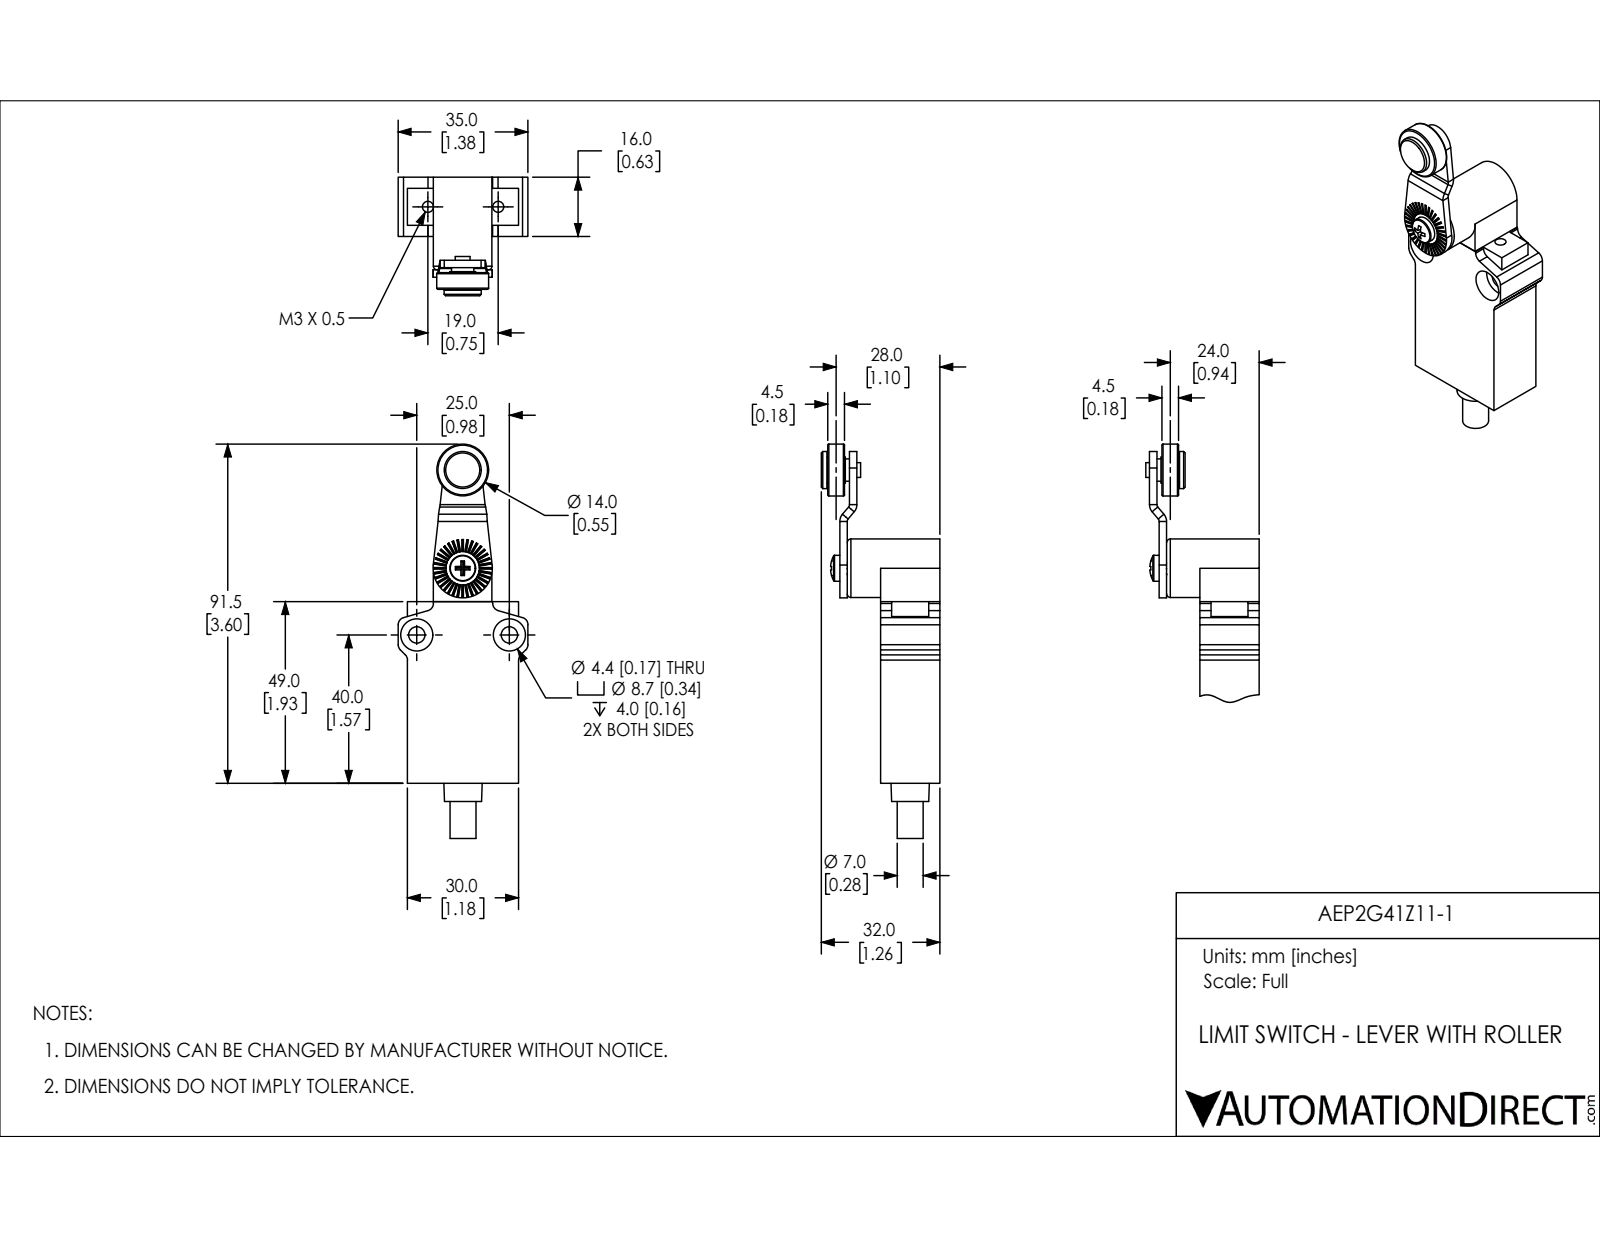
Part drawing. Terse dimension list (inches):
name: AEP2G41Z11-1
written by: SolidWorks 2018 (AUTOMOTIVE_DESIGN)
unit: in
bodies: 6 solids, 584 faces (295 planar, 117 cylindrical, 172 other)
size: 4.189 × 1.378 × 1.26
volume: 1.859 in³; area: 17.53 in²
holes: 2× ⌀0.118, 2× ⌀0.173, 2× ⌀0.343, 1× ⌀0.098, 1× ⌀0.161, 1× ⌀0.197, 1× ⌀0.224
bosses: 3× ⌀0.276, 1× ⌀0.622, 1× ⌀0.551, 1× ⌀0.394, 1× ⌀0.236, 1× ⌀0.157, 1× ⌀0.138
rounds: 8× R0.079, 2× R0.039, 2× R0.118, 1× R0.256, 1× R0.315
face distances: 0.63, 1.181, 0.354, 1.929, 0.079, 0.984, 0.102, 0.472, 0.906, 0.276
hole spacings: 0.748, 0.861, 0.865, 0.984, 1.043, 1.819, 1.821
